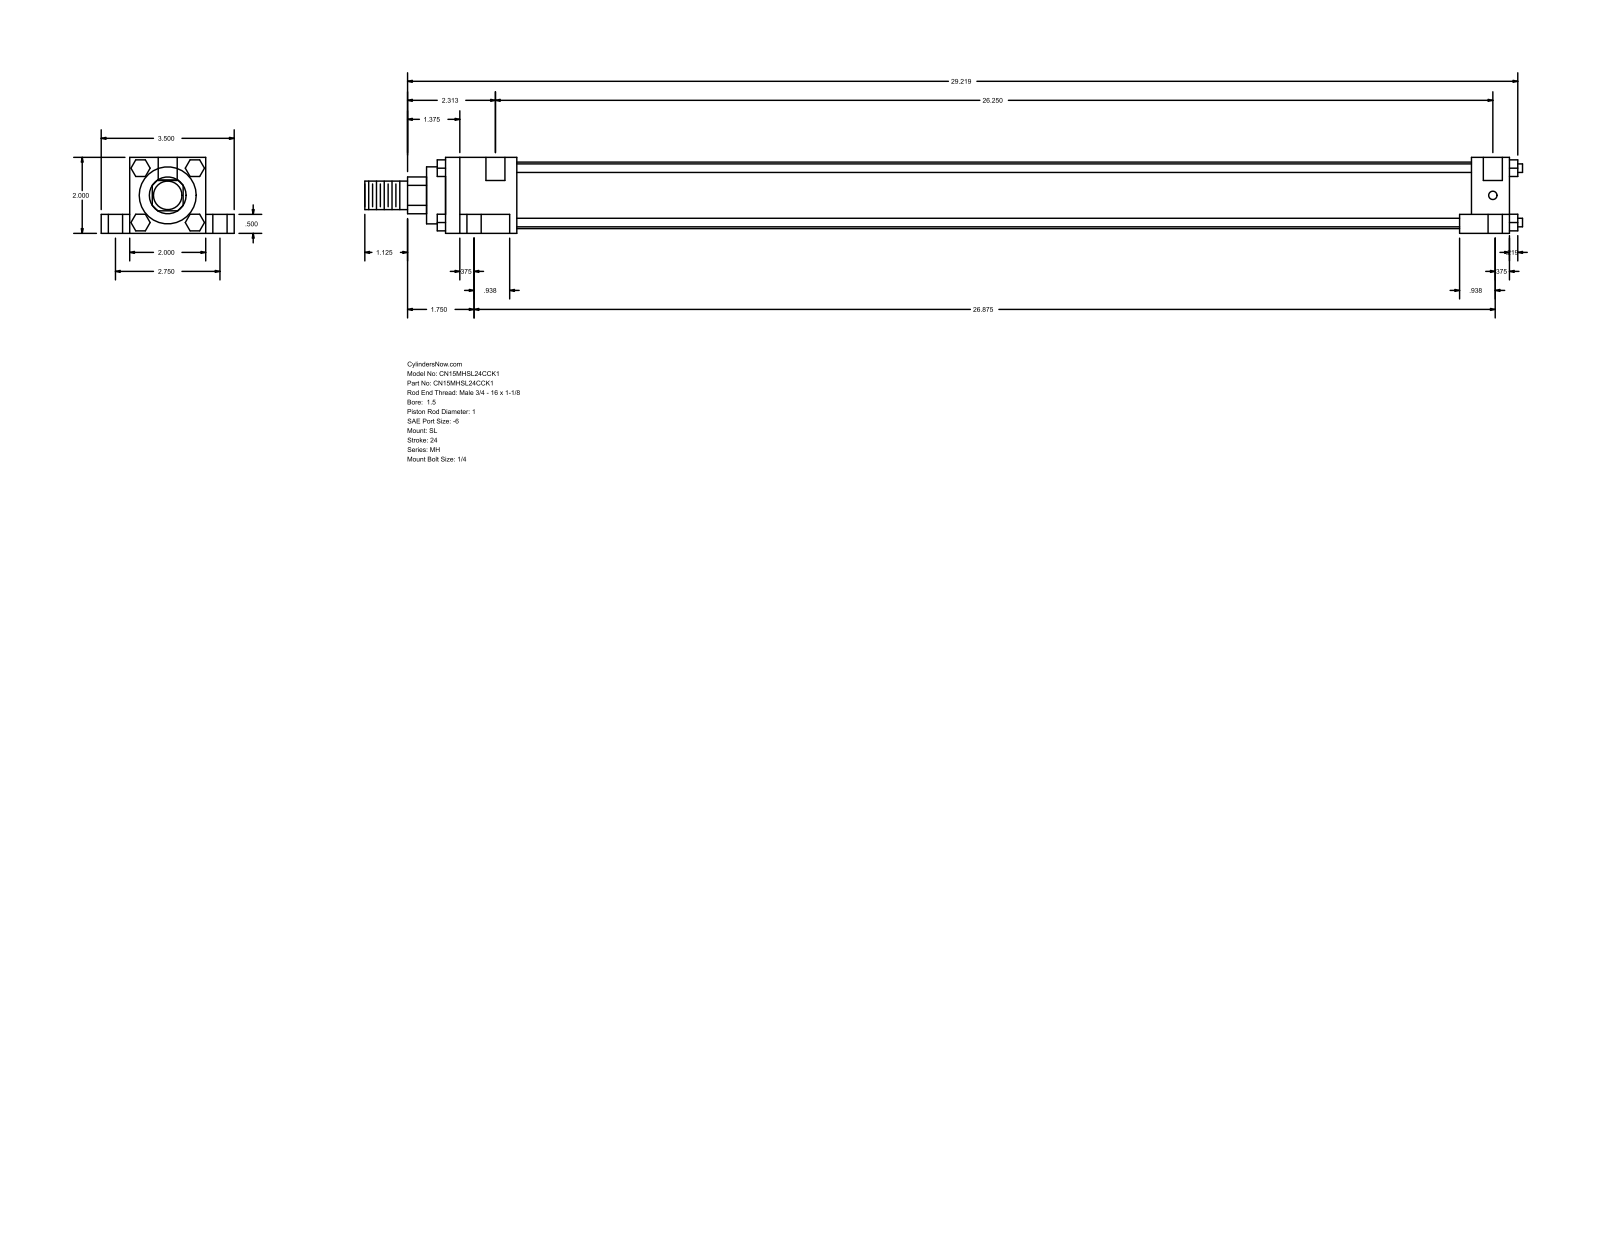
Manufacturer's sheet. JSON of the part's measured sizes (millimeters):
{"part_name": "MH_SL__0150_1", "step_written_by": "GSSL Pune (CONFIG_CONTROL_DESIGN)", "units": "millimeters", "bodies": {"solids": 0, "faces": 148, "planar": 112, "cylindrical": 36, "other": 0}, "overall_size": [773.91, 88.9, 50.8], "round_holes": [[5.56, 4], [9.53, 4], [15.88, 4], [12.7, 2]], "round_bosses_or_shafts": [[5.71, 4], [44.45, 1], [38.1, 1], [25.4, 1], [19.05, 1]], "partial_cylinders_radius": [[12.29, 1]], "face_to_face_distances": [50.8, 12.7, 38.1, 19.05, 69.85, 711.2, 25.4, 9.52, 33.34, 668.34], "hole_center_spacings": [34.96, 36.64, 37.73, 69.84, 669.25, 669.93, 672.43, 681.93]}
